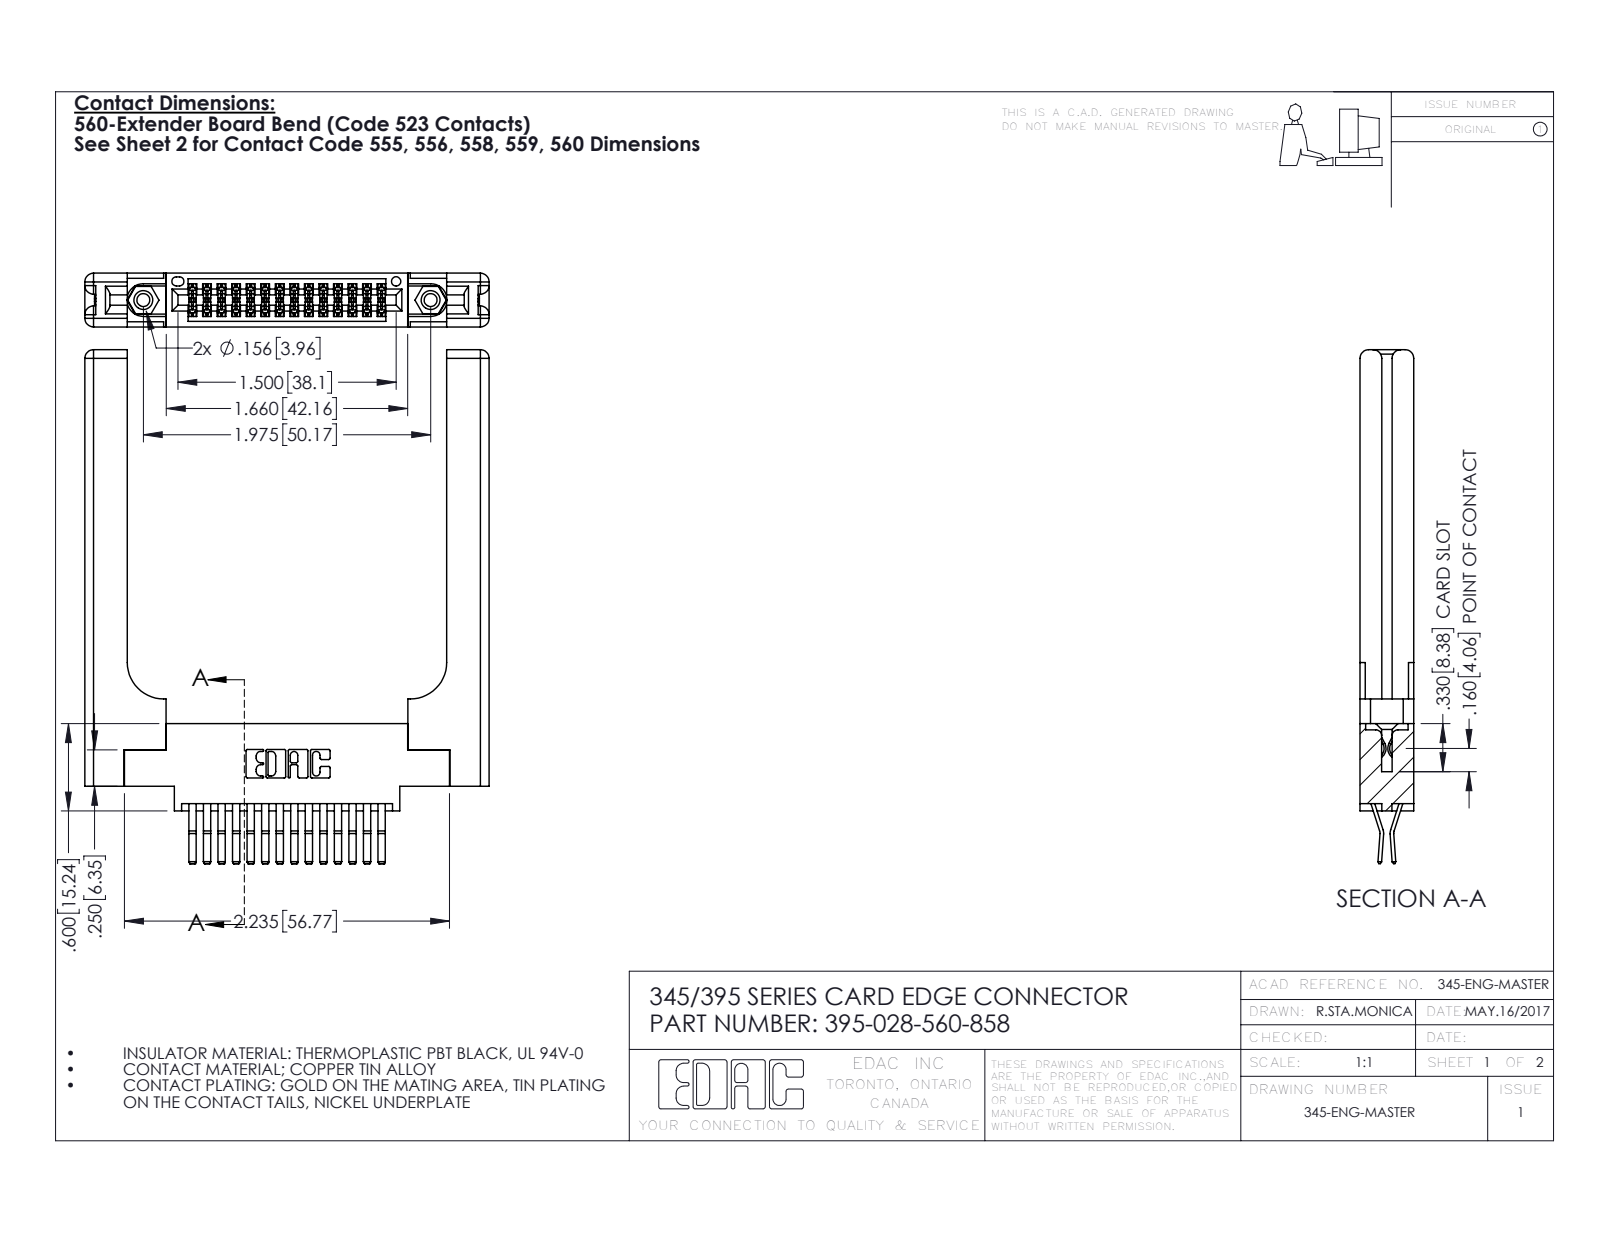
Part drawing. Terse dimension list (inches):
name: 345-220-058_345-220-058; 395-028-560-858; 345 Part_0.170 Offset - 0.156 Dia-TH; 345-292-001_560 Tail (+1 more)
written by: SolidWorks 2016 (CONFIG_CONTROL_DESIGN)
unit: in
bodies: 33 solids, 1842 faces (1156 planar, 626 cylindrical, 60 other)
size: 3.532 × 2.779 × 0.37
volume: 0.924 in³; area: 23.23 in²
holes: 2× ⌀0.089, 2× ⌀0.125, 2× ⌀0.156, 1× ⌀0.064
bosses: 2× ⌀0.155
rounds: 43× R0.006, 22× R0.01, 16× R0.06, 6× R0.007, 6× R0.031, 3× R0.026, 2× R0.01, 2× R0.014
face distances: 0.37, 0.072, 0.298, 0.025, 0.148, 0.15, 0.077, 0.22, 0.225, 0.12
hole spacings: 0.27, 1.742, 1.975
